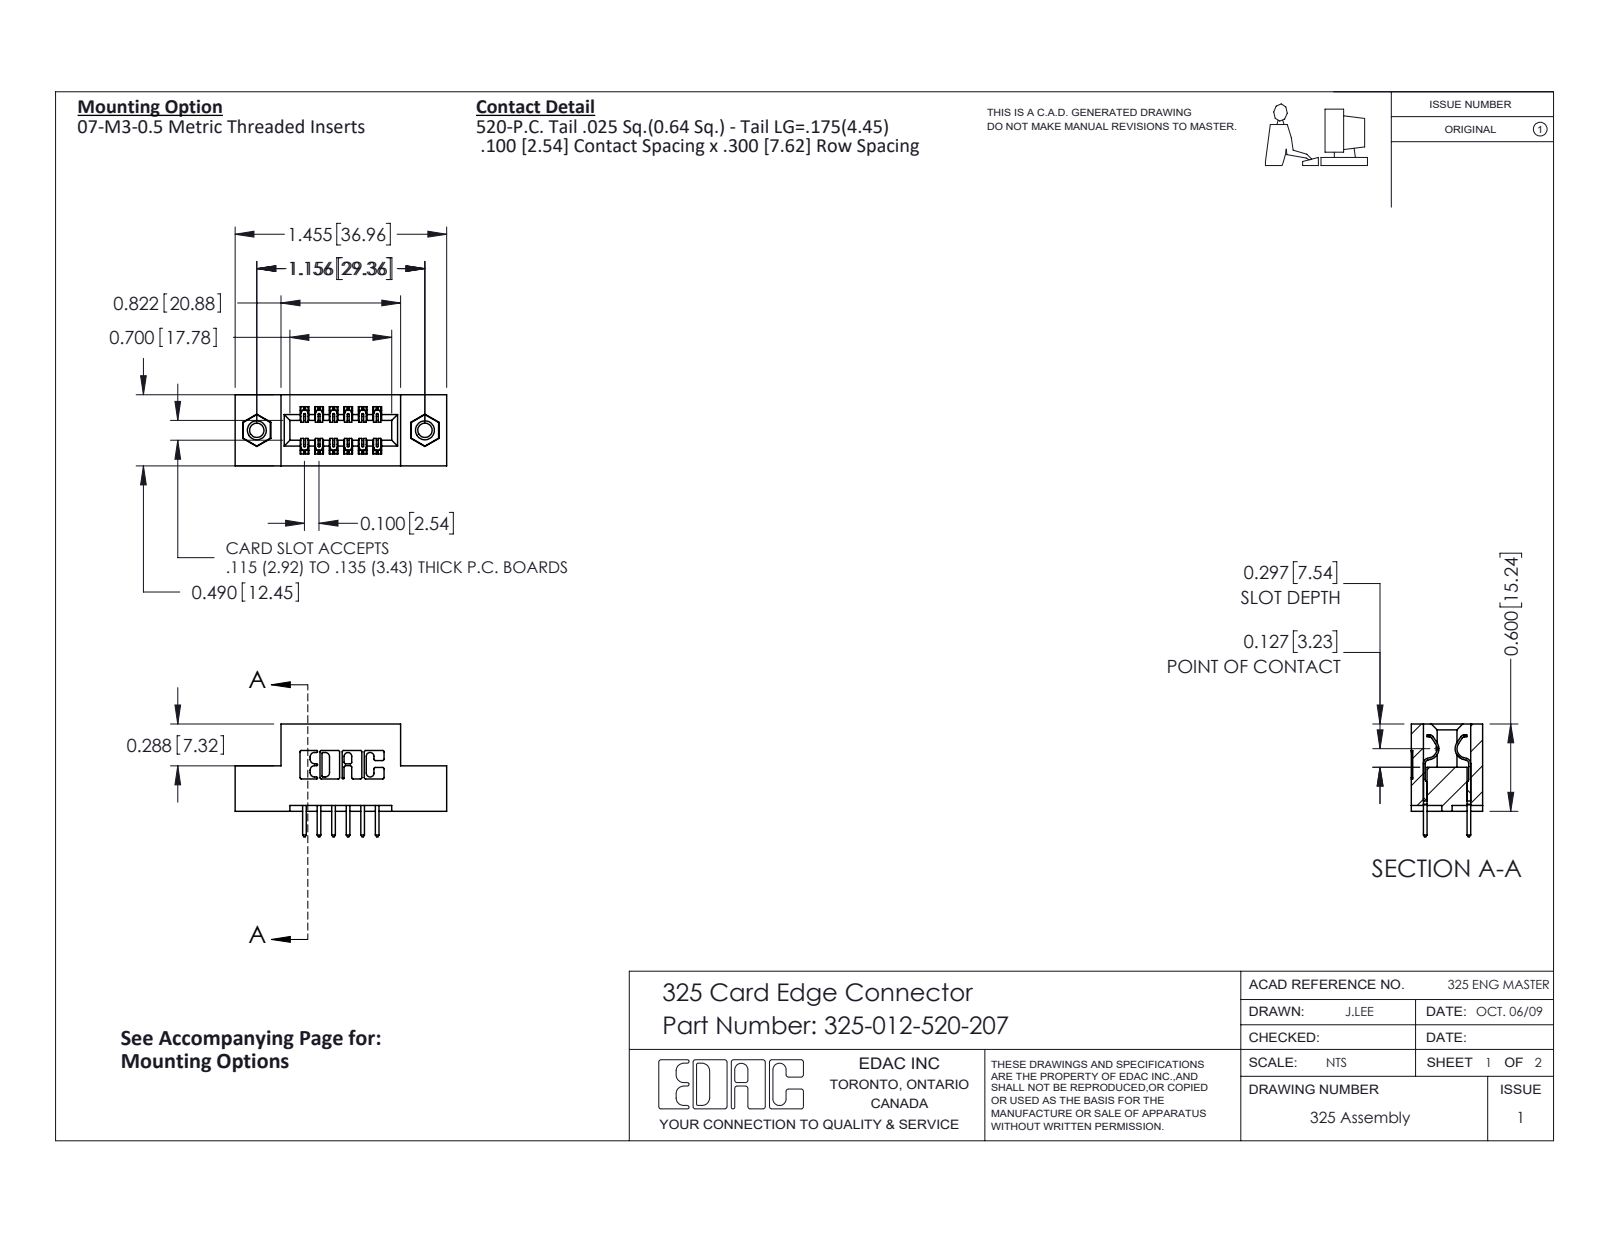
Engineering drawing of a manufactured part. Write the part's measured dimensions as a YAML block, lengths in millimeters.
part_name: "325 Part_TI; 325-292-001_325-293-120; 345-250-001_345-250-005-103; 325-012-520-207"
step_written_by: "SolidWorks 2016 (CONFIG_CONTROL_DESIGN)"
units: millimeters
bodies: {solids: 15, faces: 798, planar: 534, cylindrical: 248, other: 16}
overall_size: [37, 19.7, 12.4]
volume: 4420
surface_area: 4514
round_holes:
  - {diameter: 2.5, count: 2}
  - {diameter: 3.2, count: 2}
  - {diameter: 4.1, count: 2}
round_bosses_or_shafts:
  - {diameter: 3.9, count: 2}
partial_cylinders:
  - {radius: 0.3, count: 22}
  - {radius: 0.2, count: 18}
  - {radius: 0.3, count: 12}
  - {radius: 0.2, count: 6}
  - {radius: 0.8, count: 6}
  - {radius: 0.7, count: 3}
  - {radius: 0.4, count: 2}
  - {radius: 0.6, count: 2}
face_to_face_distances: [7.6, 2.5, 2.1, 10.3, 1, 12.4, 5.1, 1.5, 2.7, 9.7]
hole_center_spacings: [29.4]
